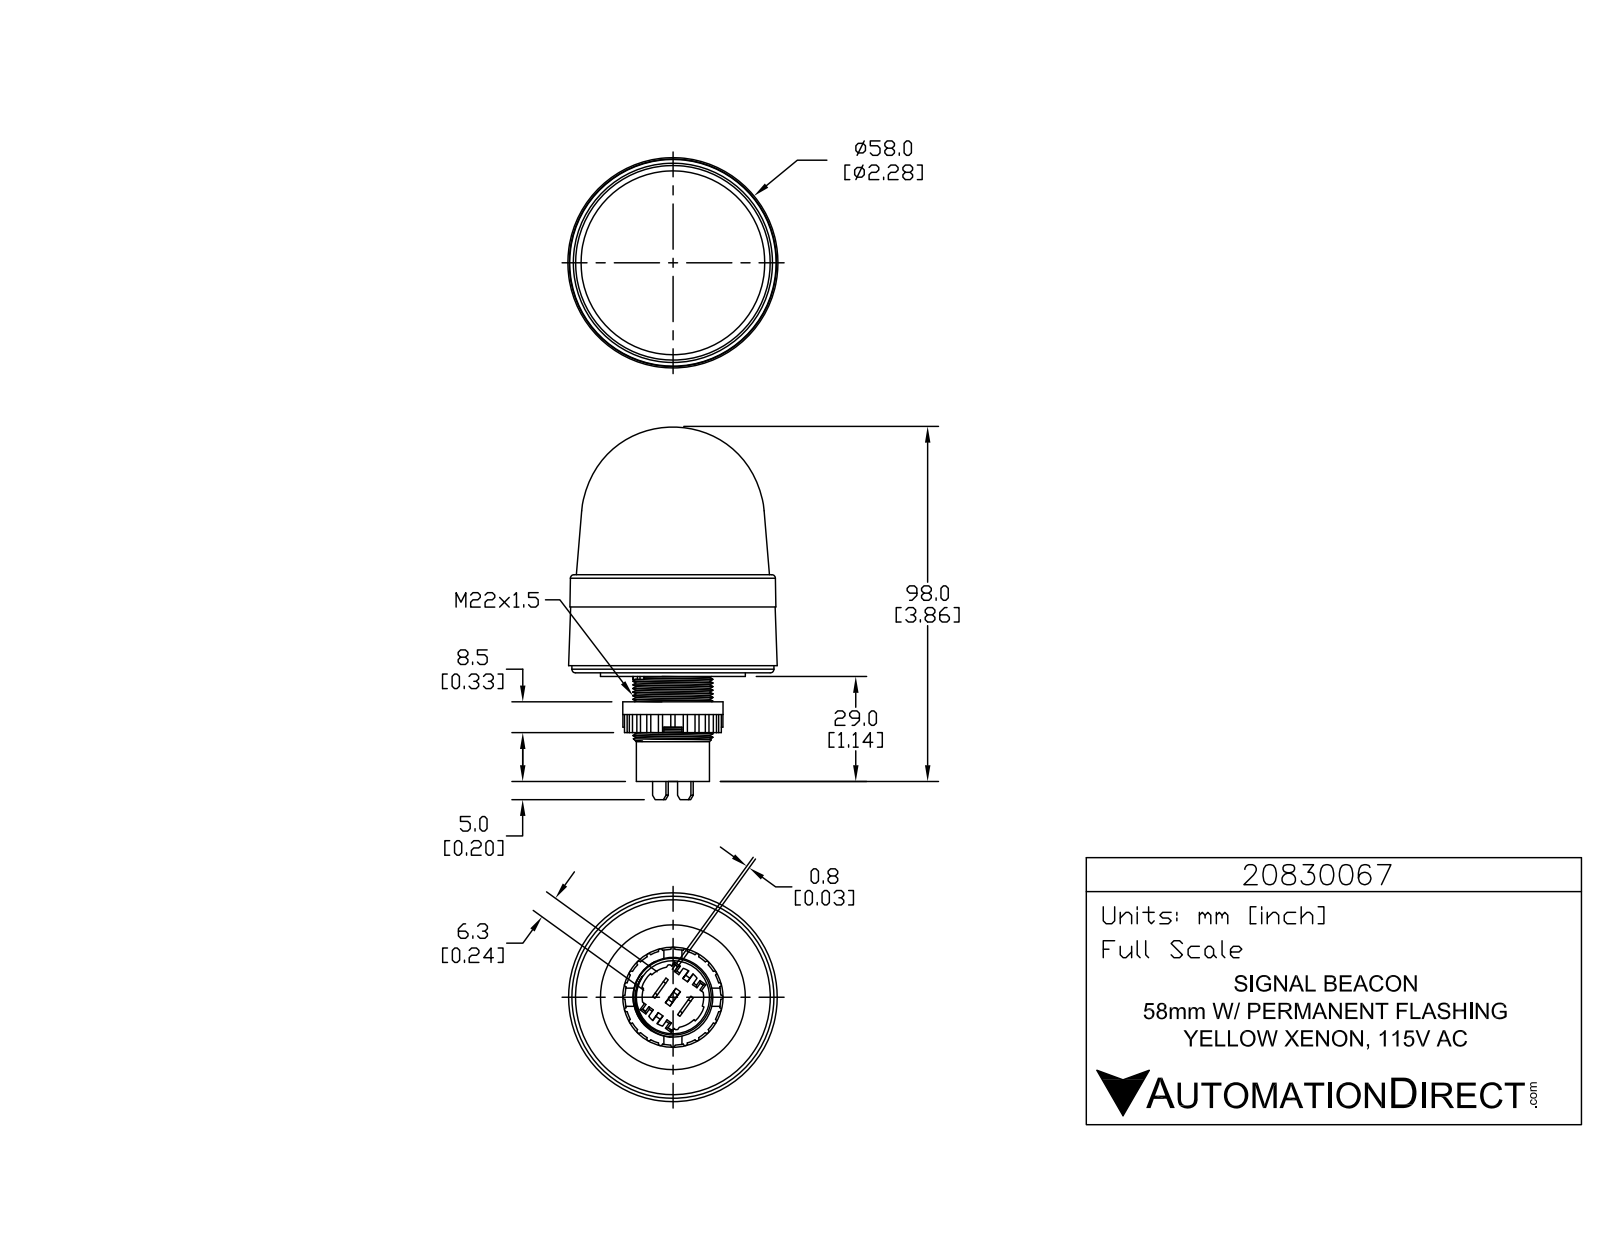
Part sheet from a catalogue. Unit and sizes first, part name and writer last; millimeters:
Units: millimetres
Overall size (bounding box): 102.9 × 57.6 × 57.6
Round holes (diameter × count): ⌀23 ×1
Round bosses / shafts (diameter × count): ⌀55.8 ×1, ⌀40 ×1, ⌀27.7 ×1, ⌀22 ×1, ⌀20.2 ×1
Partial cylindrical surfaces — rounded edges, fillets, slot ends (radius × count): R0.6 ×24, R0.5 ×2, R8.5 ×1, R9 ×1, R13.3 ×1
Main face-to-face distances: 1, 7, 3, 29, 8.5, 8, 27, 19, 26, 18.5
Volume: 147 700 mm³ · Surface area: 20 030 mm²
Bodies: 1 solid, 266 faces (119 planar, 120 cylindrical, 27 other)
Part name (STEP PRODUCT): 20830067
STEP written by: SolidWorks 2015 (AUTOMOTIVE_DESIGN)
